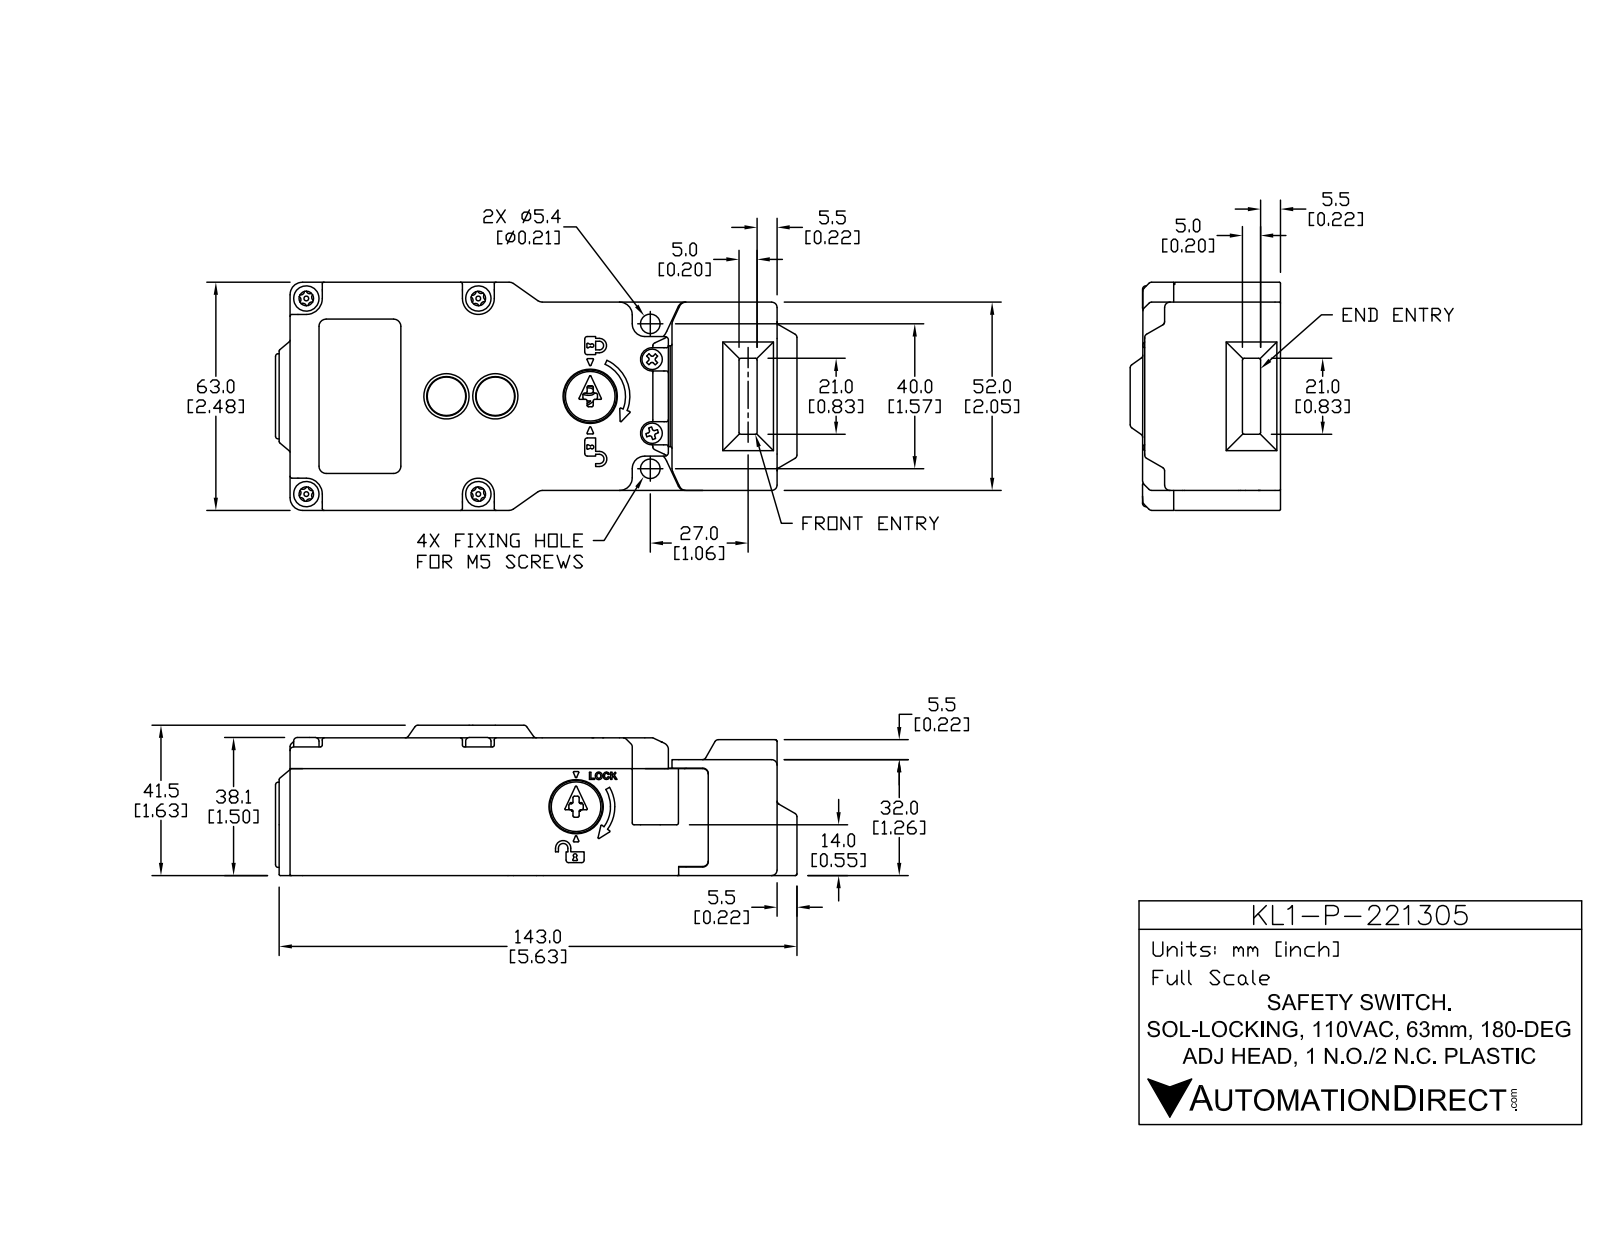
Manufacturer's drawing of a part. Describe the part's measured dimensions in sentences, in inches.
The part is named "KL1-P-221305". Its 3-D file was written by "SolidWorks 2017 (AUTOMOTIVE_DESIGN)". It is 18 solids with 3047 faces: 909 planar, 1225 cylindrical and 913 other. Overall it measures 5.669 by 2.48 by 1.634 inches. Its volume is 6.348 cubic inches and its surface area 118.8 square inches. Round holes: 4 of diameter 0.102, 4 of diameter 0.134, 4 of diameter 0.157, 4 of diameter 0.161, 4 of diameter 0.177, 4 of diameter 0.197, 2 of diameter 0.079, 2 of diameter 0.083, 2 of diameter 0.118, 2 of diameter 0.126, 2 of diameter 0.142, 2 of diameter 0.264. Round bosses or shafts: 4 of diameter 0.276, 4 of diameter 0.138, 4 of diameter 0.051, 3 of diameter 0.197, 3 of diameter 0.039, 2 of diameter 0.571, 2 of diameter 0.417, 2 of diameter 0.362. Partial cylindrical surfaces (rounded edges, fillets, slot ends): 348 of radius 0.02, 126 of radius 0.012, 106 of radius 0.039, 30 of radius 0.008, 24 of radius 0.016, 16 of radius 0.059, 14 of radius 0.006, 12 of radius 0.028. The main face-to-face distances are 0.098, 0.118, 0.217, 1.496, 1.398, 1.402, 1.303, 0.094, 2.264, 2.146. The hole center spacings are 0.404, 0.498, 0.515, 0.549, 0.784, 0.803, 1.079, 1.118.
